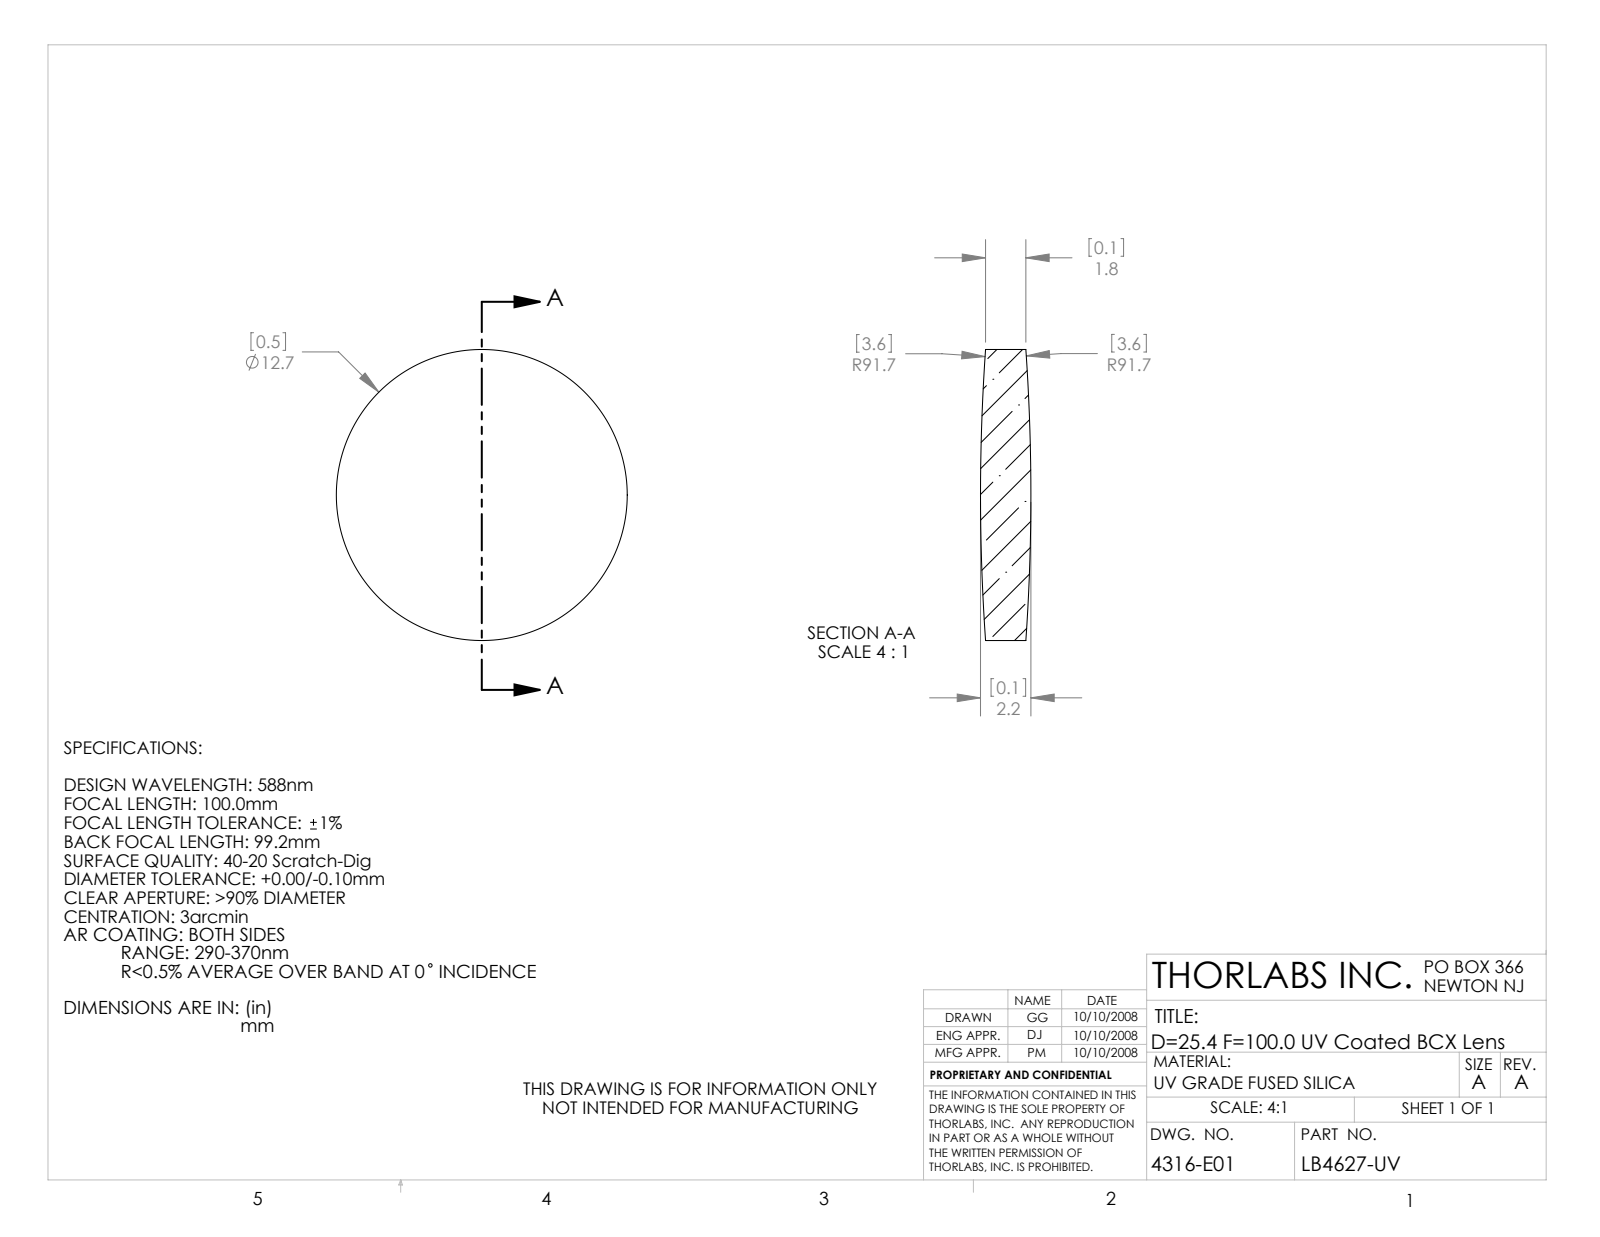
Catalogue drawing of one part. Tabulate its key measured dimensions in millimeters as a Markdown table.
| quantity | value |
| --- | --- |
| part name | 4316-E0W |
| STEP written by | SolidWorks 2007 (CONFIG_CONTROL_DESIGN) |
| units | millimeters |
| bodies | 1 solid, 6 faces (0 planar, 2 cylindrical, 4 other) |
| overall size | 12.7 × 12.7 × 2.2 |
| volume | 251 mm³ |
| surface area | 324 mm² |
| round bosses / shafts (diameter × count) | 12.7 × 1 |
